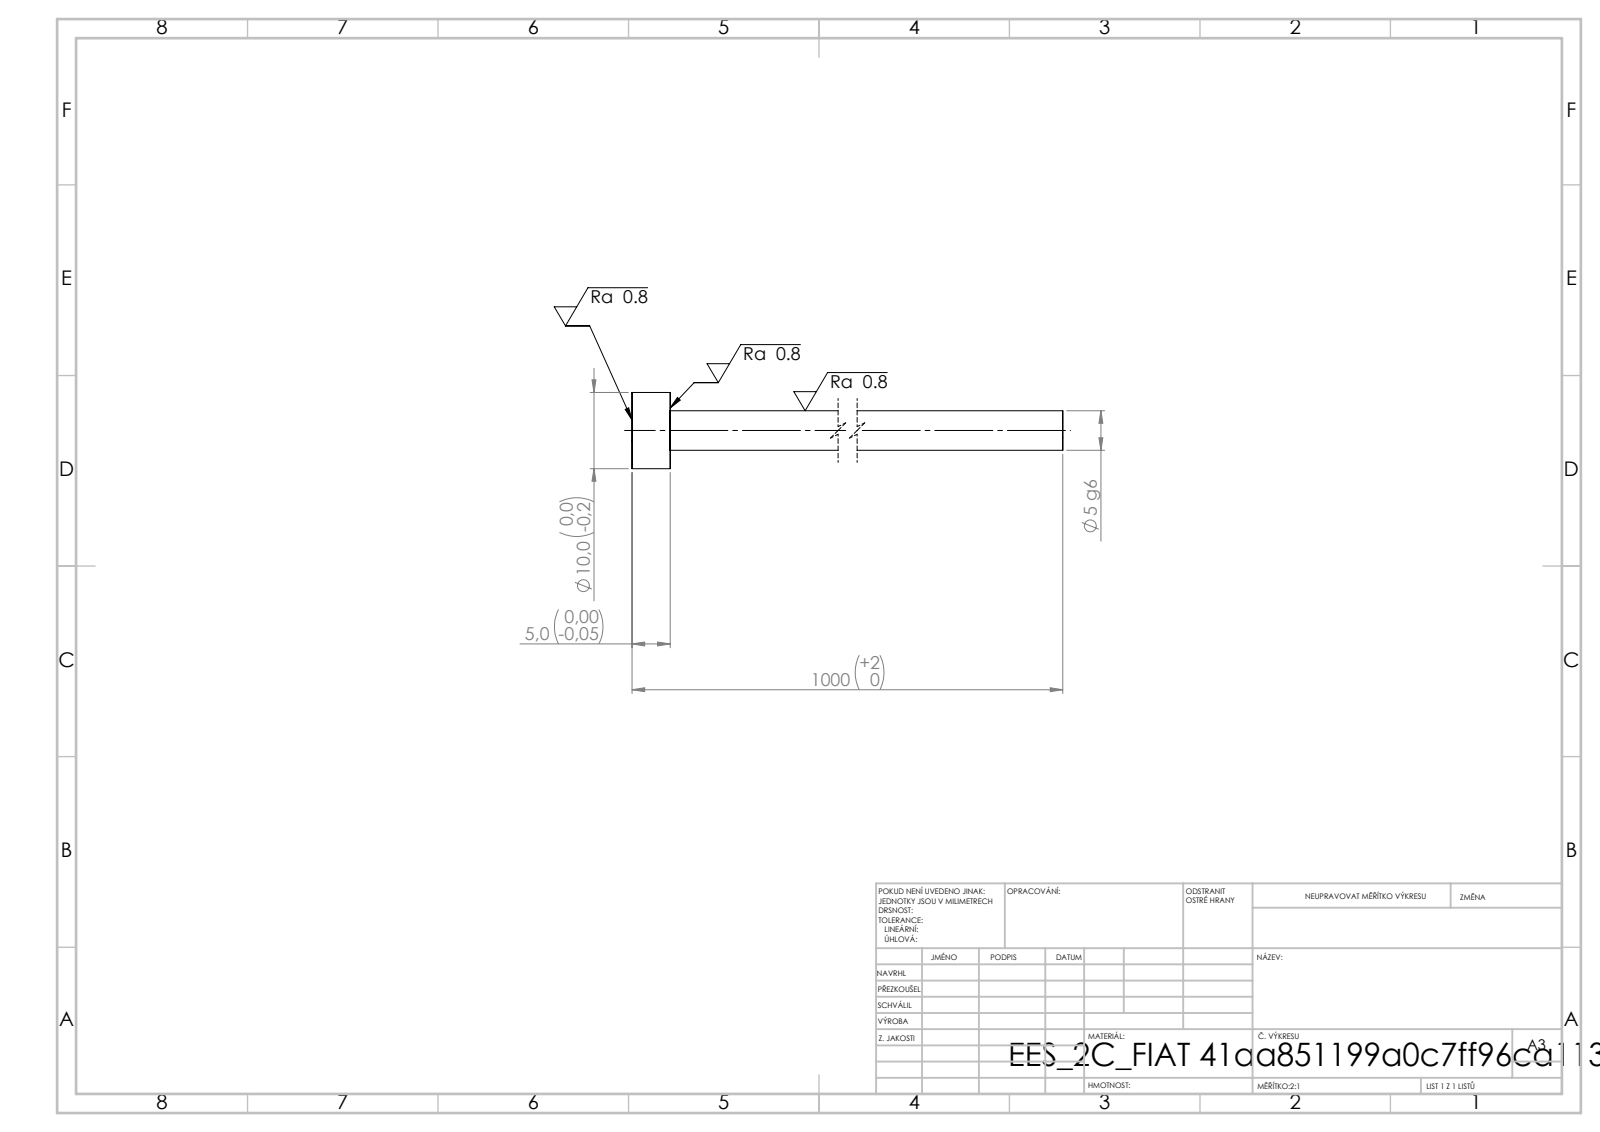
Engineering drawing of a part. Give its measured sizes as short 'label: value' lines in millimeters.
written by: SolidWorks 2019 (CONFIG_CONTROL_DESIGN)
unit: mm
bodies: 1 solid, 7 faces (3 planar, 4 cylindrical, 0 other)
size: 1000 × 10 × 10
volume: 21 524 mm³; area: 16 569 mm²
bosses: 1× ⌀10, 1× ⌀5.2
face distances: 5, 1000, 995
